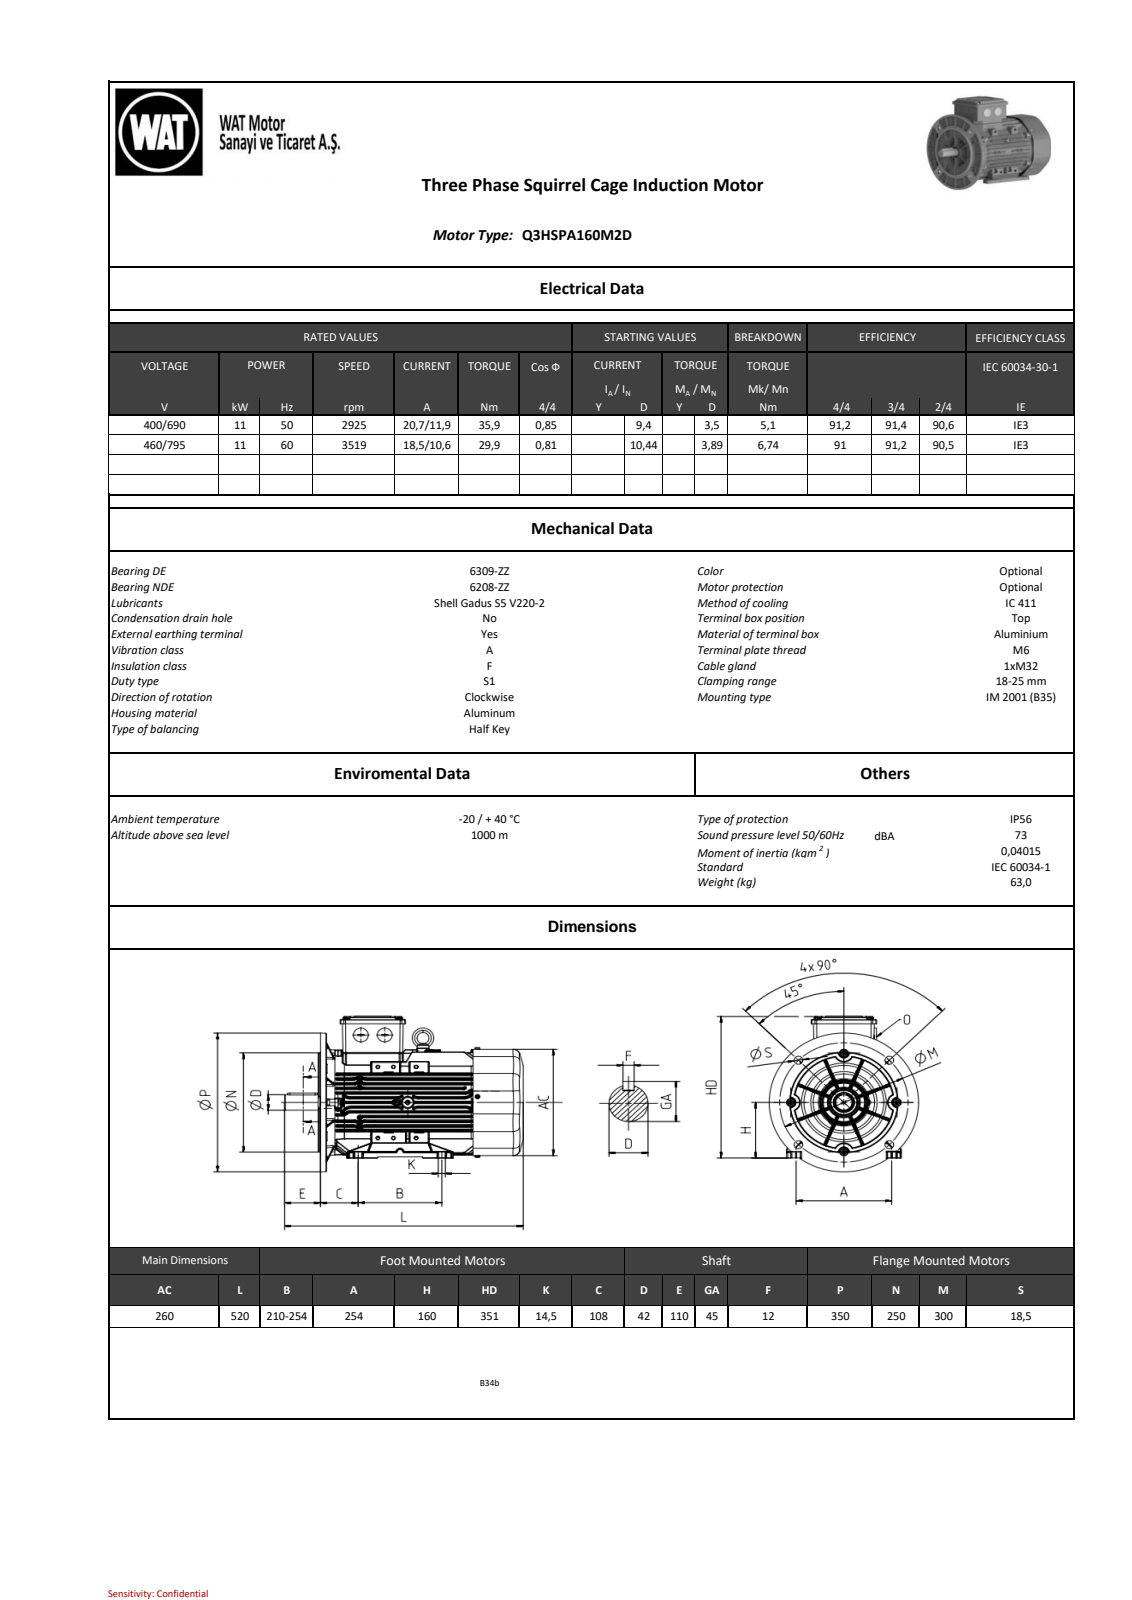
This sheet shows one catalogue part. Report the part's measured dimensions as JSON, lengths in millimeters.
{"part_name": "QHS series_ 160_B35_stp_objects", "step_written_by": "SIEMENS PLM Software NX2206.8101 (AP203_CONFIGURATION_CONTROLLED_3D_DESIGN_OF_MECHANICAL_PARTS_AND_ASSEMBLIES_MIM_LF)", "units": "millimeters", "bodies": {"solids": 0, "faces": 7216, "planar": 1714, "cylindrical": 3210, "other": 2292}, "overall_size": [519.49, 374.4, 349.89], "round_holes": [[17, 5], [5.5, 4], [6.8, 2], [8, 2], [8.48, 1], [8.48, 1], [16, 1], [62, 1], [68.67, 1], [82, 1], [180, 1], [223, 1]], "round_bosses_or_shafts": [[8, 3], [38, 2], [13, 2], [250, 1], [230.5, 1], [86.77, 1], [45, 1], [42, 1]], "partial_cylinders_radius": [[1, 806], [0.8, 805], [2, 208], [3, 84], [0.5, 64], [7, 48], [5, 37], [1.5, 32]], "face_to_face_distances": [1.5, 10.42, 10.56, 14, 20.84, 10.28, 7, 125.58, 84.04, 94.46], "hole_center_spacings": [74.95, 106, 120.5, 170.41, 149.91, 241, 217.51]}
